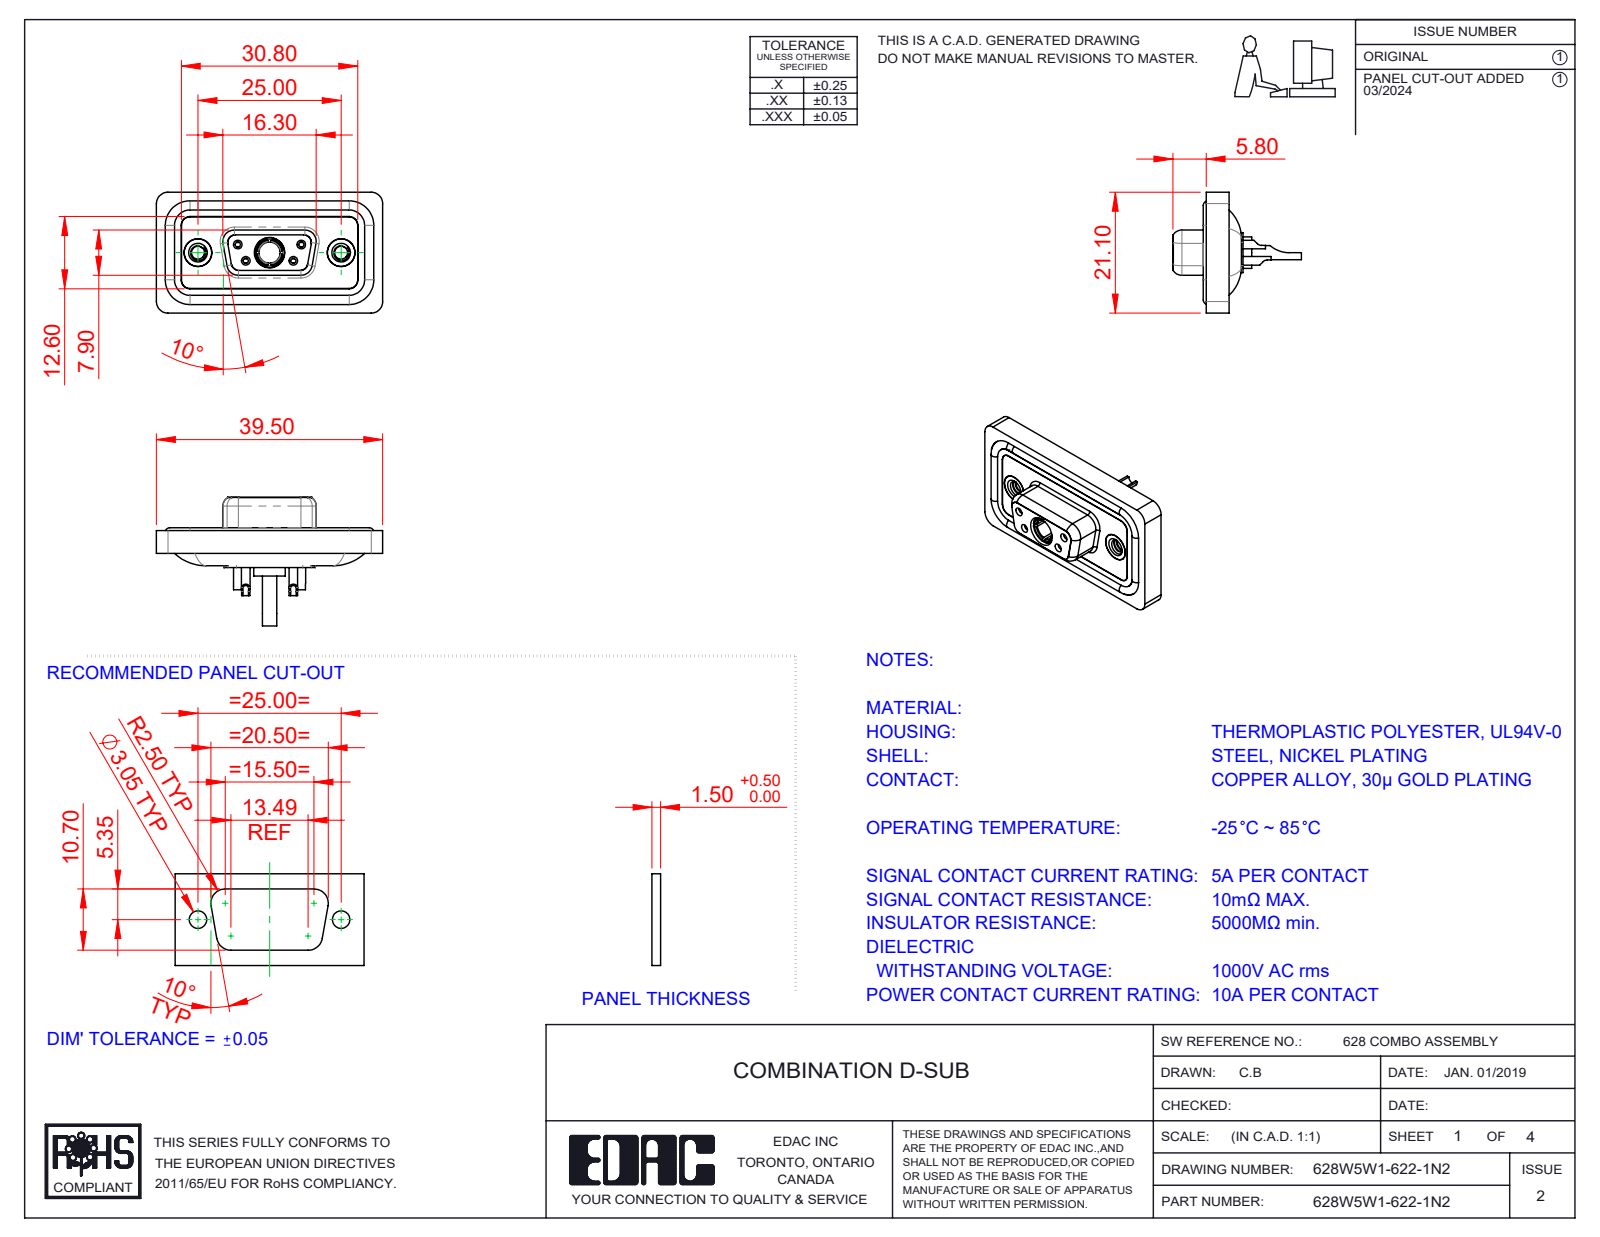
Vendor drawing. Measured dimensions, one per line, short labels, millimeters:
name: 628Combo Contact Row 1_22; 628Combo Shell Rear_09 Contacts; 628Combo Waterproof Housing_09 Contacts; Power Socket_10A SC (+5 more)
written by: SolidWorks 2023 (CONFIG_CONTROL_DESIGN)
unit: mm
bodies: 13 solids, 685 faces (204 planar, 298 cylindrical, 183 other)
size: 39.5 × 22.45 × 21.1
volume: 4 772 mm³; area: 7 725 mm²
holes: 4× ⌀0.9, 4× ⌀1, 4× ⌀1.1, 4× ⌀1.5, 4× ⌀2, 3× ⌀4.85, 2× ⌀1.6, 2× ⌀1.7, 2× ⌀2.26, 2× ⌀4, 2× ⌀4.05, 2× ⌀5
bosses: 6× ⌀1.6, 4× ⌀2.2, 2× ⌀4.95, 2× ⌀4.8, 1× ⌀5.5, 1× ⌀5.2, 1× ⌀4.96, 1× ⌀4.75
rounds: 22× R1.5, 18× R2, 8× R1.35, 8× R1.6, 6× R1, 4× R0.25, 4× R0.5, 4× R0.6
face distances: 0.4, 2.9, 1.8, 1.1, 1.6, 0.5, 5.65, 7.45, 5.35, 3.6
hole spacings: 3.16, 5.72, 7.1, 12.5, 18.1, 4.39, 4.4, 8.31
